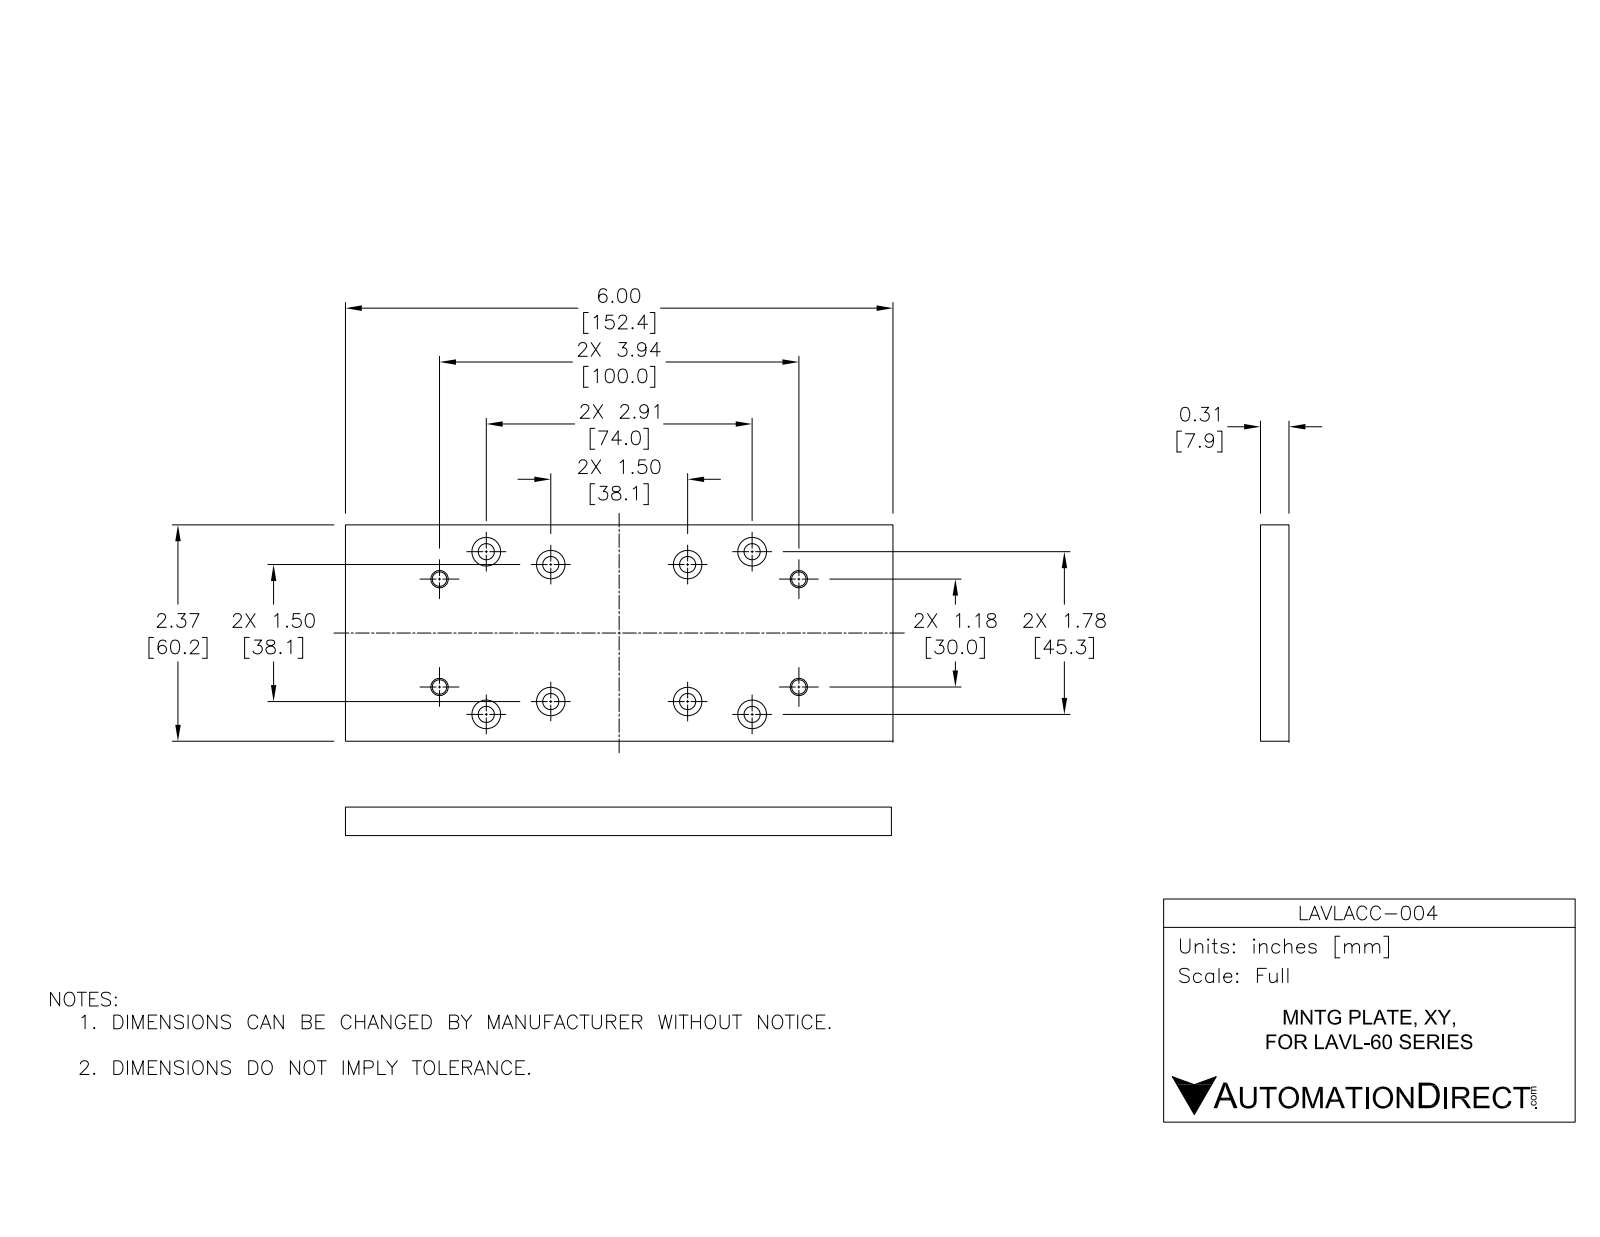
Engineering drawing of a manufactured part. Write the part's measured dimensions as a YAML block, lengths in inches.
part_name: "LAVLACC-004"
step_written_by: "SolidWorks 2015 (AUTOMOTIVE_DESIGN)"
units: inches
bodies: {solids: 1, faces: 54, planar: 14, cylindrical: 40, other: 0}
overall_size: [6, 2.371, 0.313]
volume: 4.292
surface_area: 35.7
round_holes:
  - {diameter: 0.159, count: 4}
  - {diameter: 0.177, count: 4}
  - {diameter: 0.177, count: 4}
  - {diameter: 0.313, count: 4}
  - {diameter: 0.315, count: 4}
face_to_face_distances: [0.313, 2.371, 6, 0.155, 0.157, 0.148, 0.164]
hole_center_spacings: [0.593, 0.72, 1.229, 1.5, 1.567, 1.787, 1.811, 2.211]
